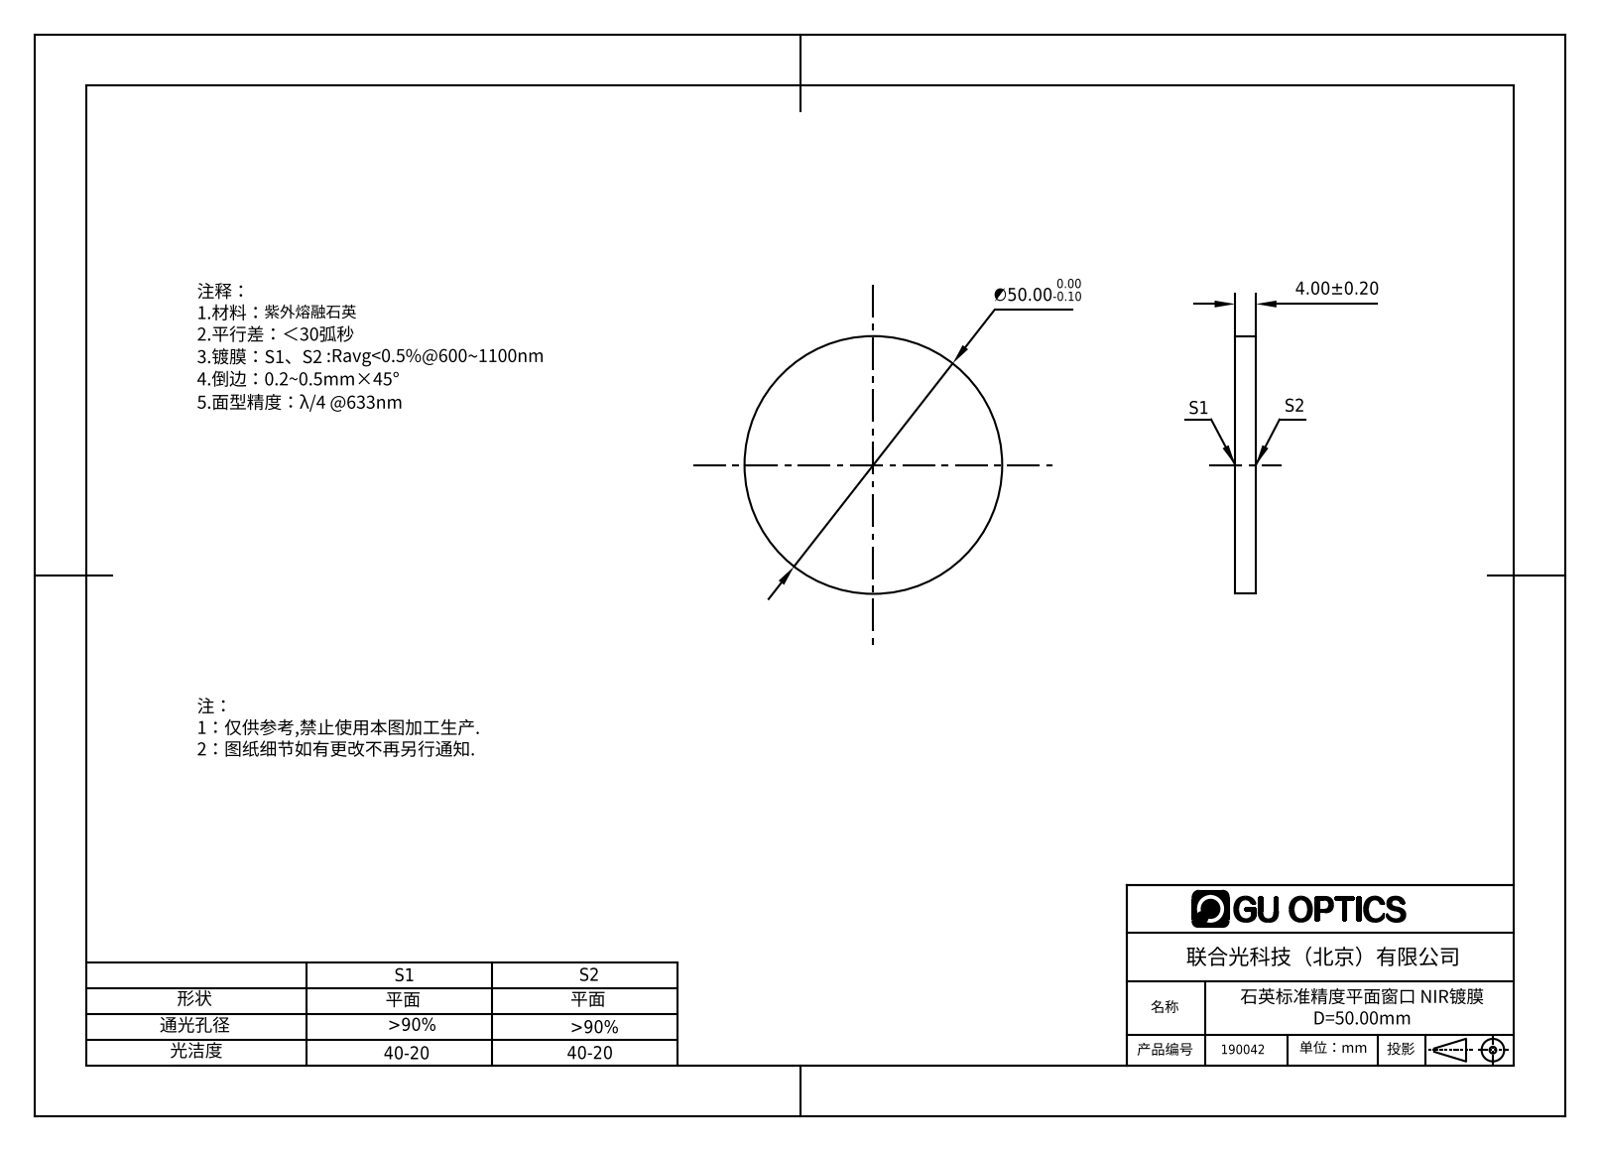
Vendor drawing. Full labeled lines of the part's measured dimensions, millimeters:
Part name (STEP PRODUCT): 180009
STEP written by: SolidWorks 2016 (AUTOMOTIVE_DESIGN)
Units: millimetres
Bodies: 1 solid, 4 faces (2 planar, 2 cylindrical, 0 other)
Overall size (bounding box): 50 × 50 × 4
Volume: 7 854 mm³ · Surface area: 4 555 mm²
Round bosses / shafts (diameter × count): ⌀50 ×1
Main face-to-face distances: 4
